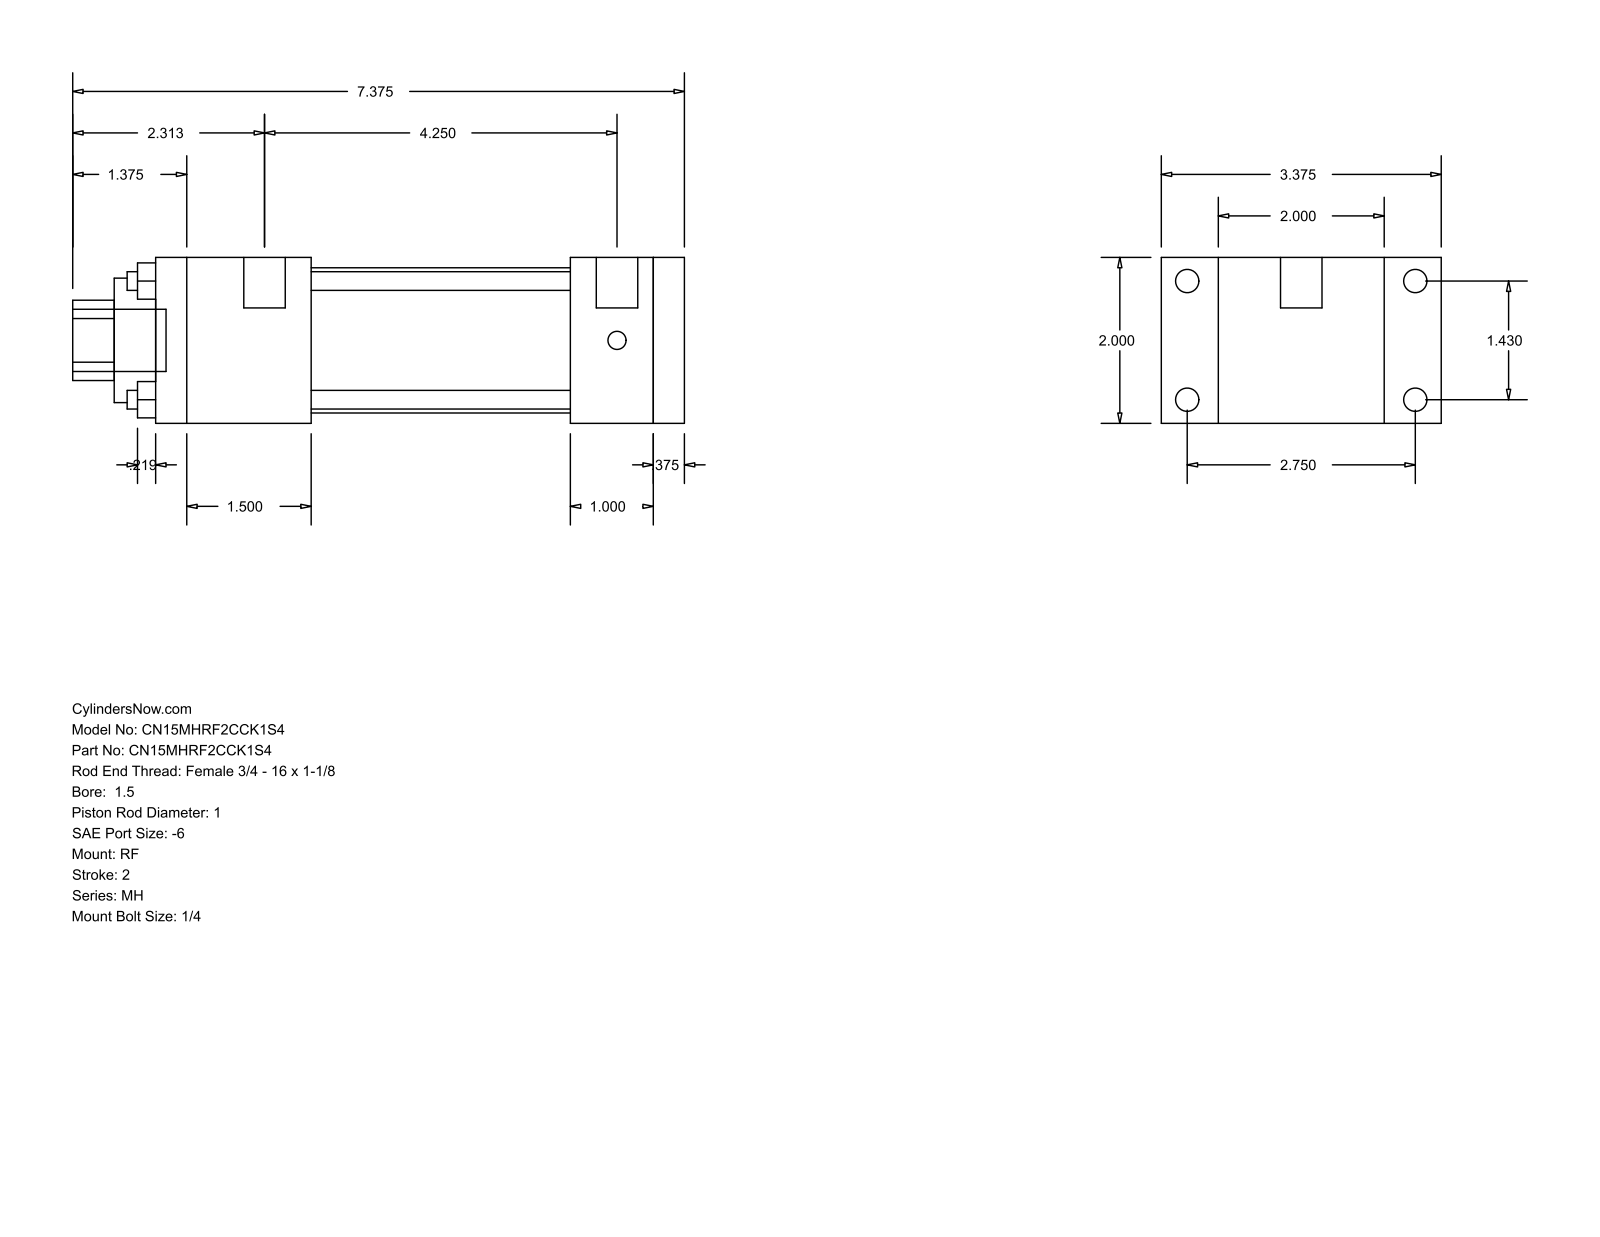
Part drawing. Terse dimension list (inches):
name: MH_RF__0150_1
written by: GSSL Pune (CONFIG_CONTROL_DESIGN)
unit: in
bodies: 0 solids, 92 faces (64 planar, 28 cylindrical, 0 other)
size: 7.375 × 3.375 × 2
holes: 4× ⌀0.225, 1× ⌀1, 1× ⌀1.5, 1× ⌀1.75
bosses: 4× ⌀0.281, 4× ⌀0.219, 2× ⌀0.5, 1× ⌀0.75
rounds: 1× R0.484
face distances: 2, 0.375, 6, 1, 6.375, 0.687, 2.687, 5, 1.375, 1.875
hole spacings: 1.011, 1.43, 2.022
